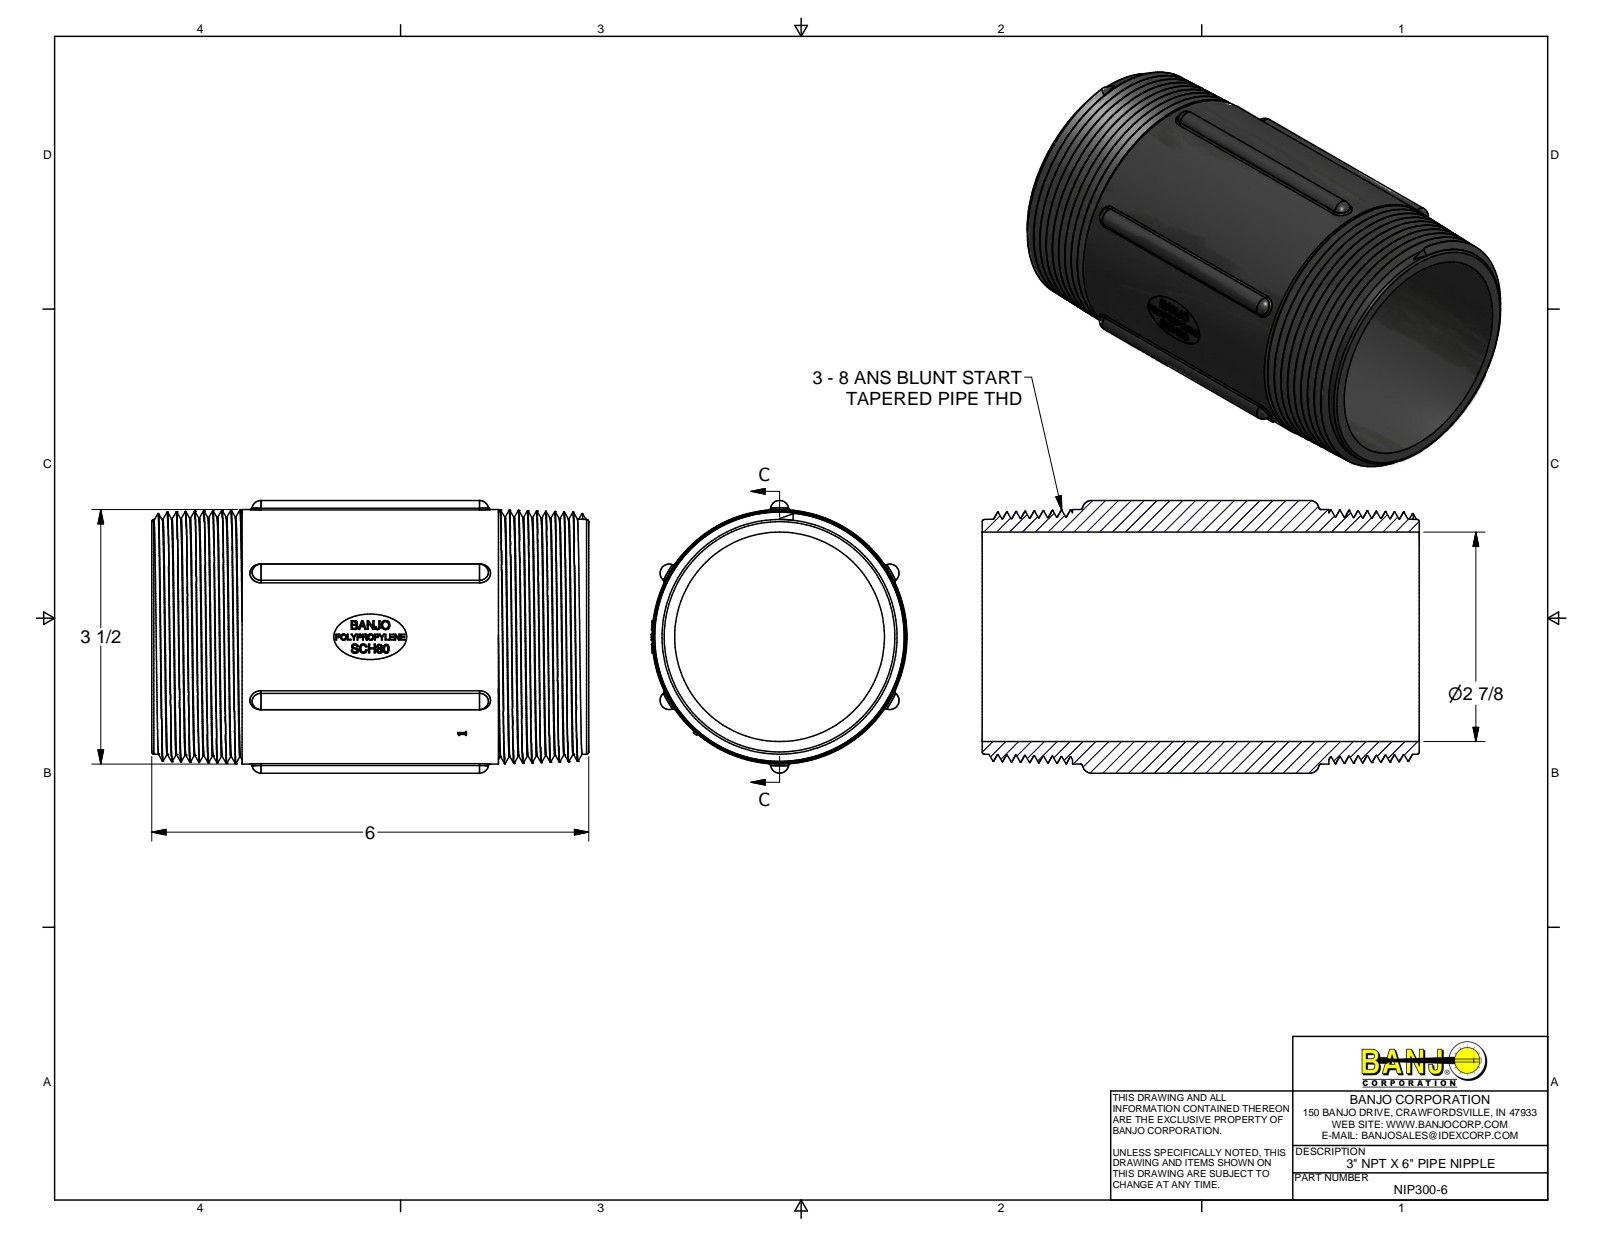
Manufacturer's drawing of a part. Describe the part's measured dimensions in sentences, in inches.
The part is named "NIP300-6". Its 3-D file was written by "Autodesk Inventor 2013 (AUTOMOTIVE_DESIGN)". It is 1 solid with 419 faces: 168 planar, 58 cylindrical and 193 other. Overall it measures 6 by 3.75 by 3.51 inches. Its volume is 17.13 cubic inches and its surface area 147.6 square inches. Round holes: 1 of diameter 2.88. Round bosses or shafts: 1 of diameter 3.5. Partial cylindrical surfaces (rounded edges, fillets, slot ends): 12 of radius 0.03, 6 of radius 0.125, 1 of radius 1.74, 1 of radius 1.76, 1 of radius 1.77. The main face-to-face distances are 6, 1.24, 4.76, 3.52, 0.015, 0.071, 0.08, 0.157, 0.152, 0.018.
